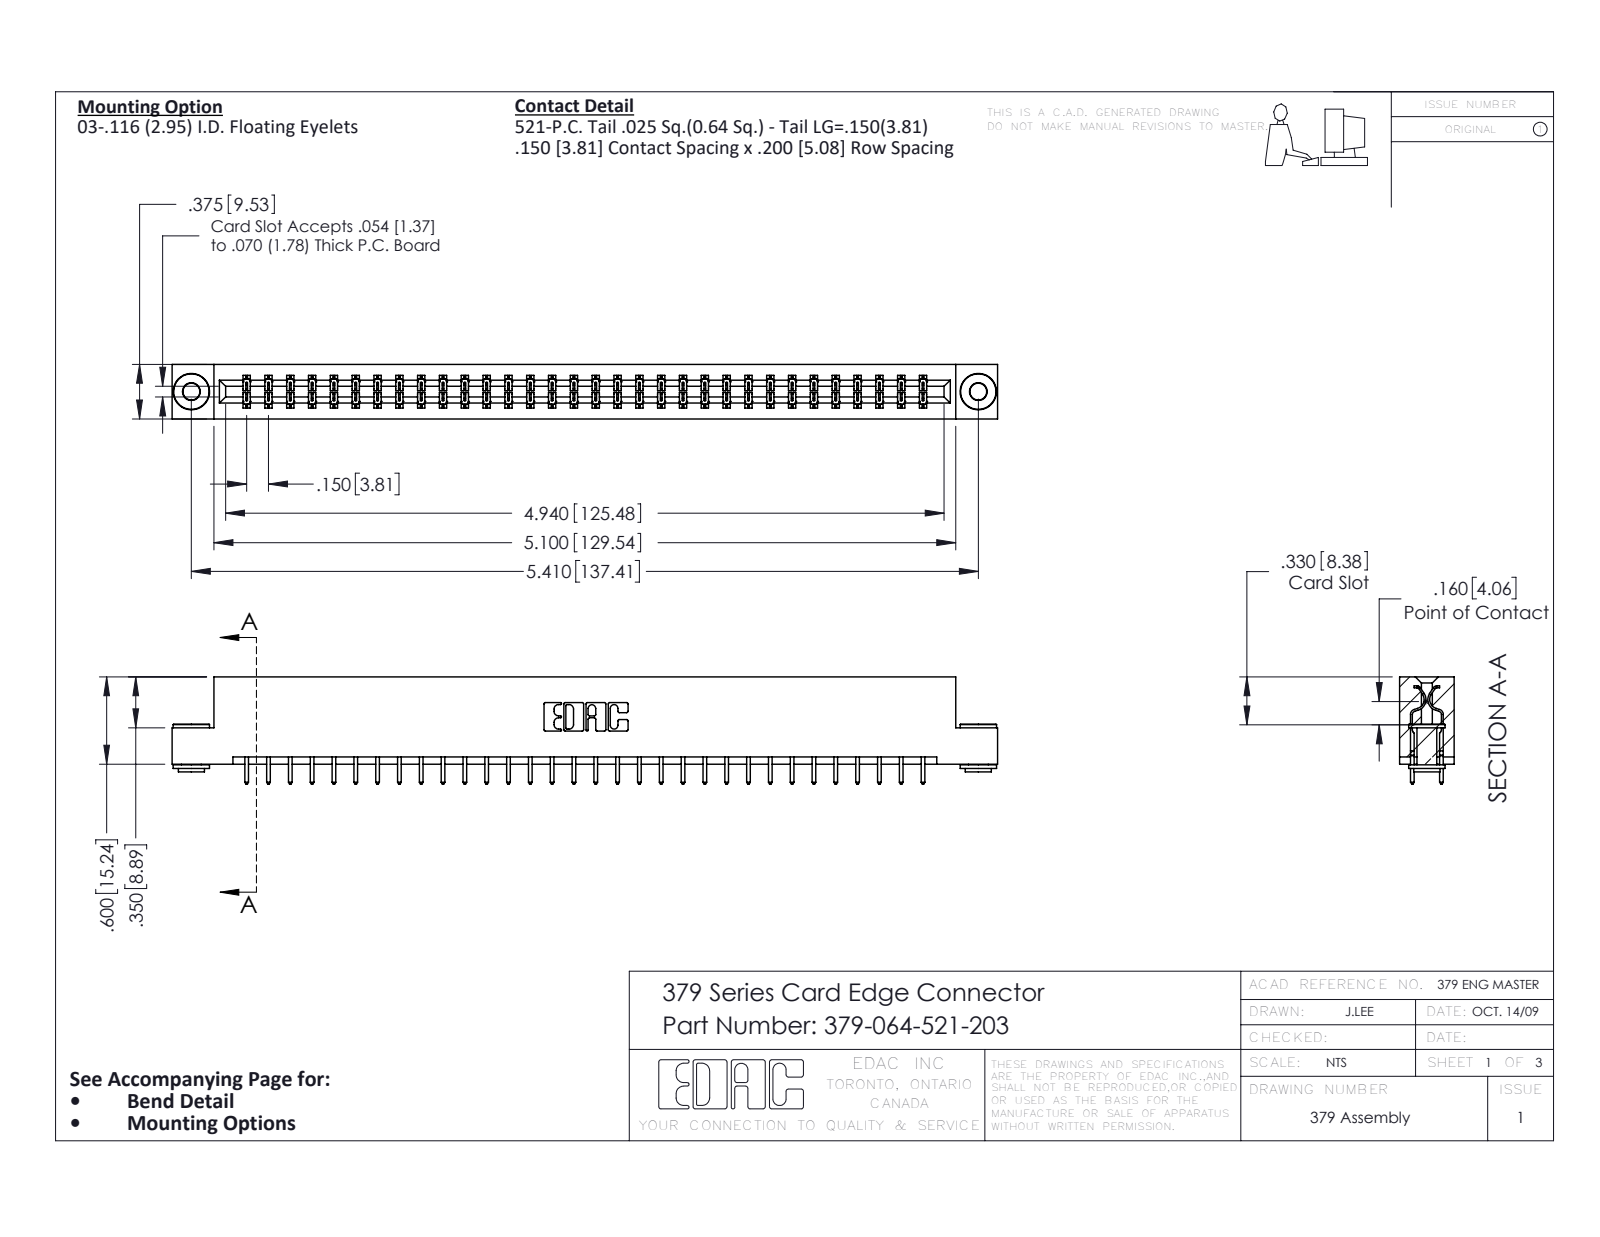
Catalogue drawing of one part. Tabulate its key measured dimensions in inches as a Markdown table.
| quantity | value |
| --- | --- |
| part name | 379-064-521-203; 345-292-001_345-293-121; 345-250-002_345-250-002-102; 379 Part_Flush - .156 Dia - TH |
| STEP written by | SolidWorks 2016 (CONFIG_CONTROL_DESIGN) |
| units | inches |
| bodies | 67 solids, 3480 faces (2384 planar, 1088 cylindrical, 8 other) |
| overall size | 5.675 × 0.737 × 0.375 |
| volume | 0.929 in³ |
| surface area | 26.42 in² |
| round holes (diameter × count) | 0.116 × 2, 0.156 × 2 |
| round bosses / shafts (diameter × count) | 0.25 × 2, 0.18 × 2, 0.136 × 2 |
| partial cylindrical surfaces (radius × count) | 0.006 × 96, 0.01 × 64, 0.01 × 22, 0.007 × 6, 0.031 × 6, 0.026 × 3, 0.014 × 2, 0.022 × 2 |
| main face-to-face distances | 0.3, 0.075, 0.375, 0.2, 0.1, 0.225, 0.275, 0.15, 0.076, 0.025 |
| hole center spacings | 5.41 |
